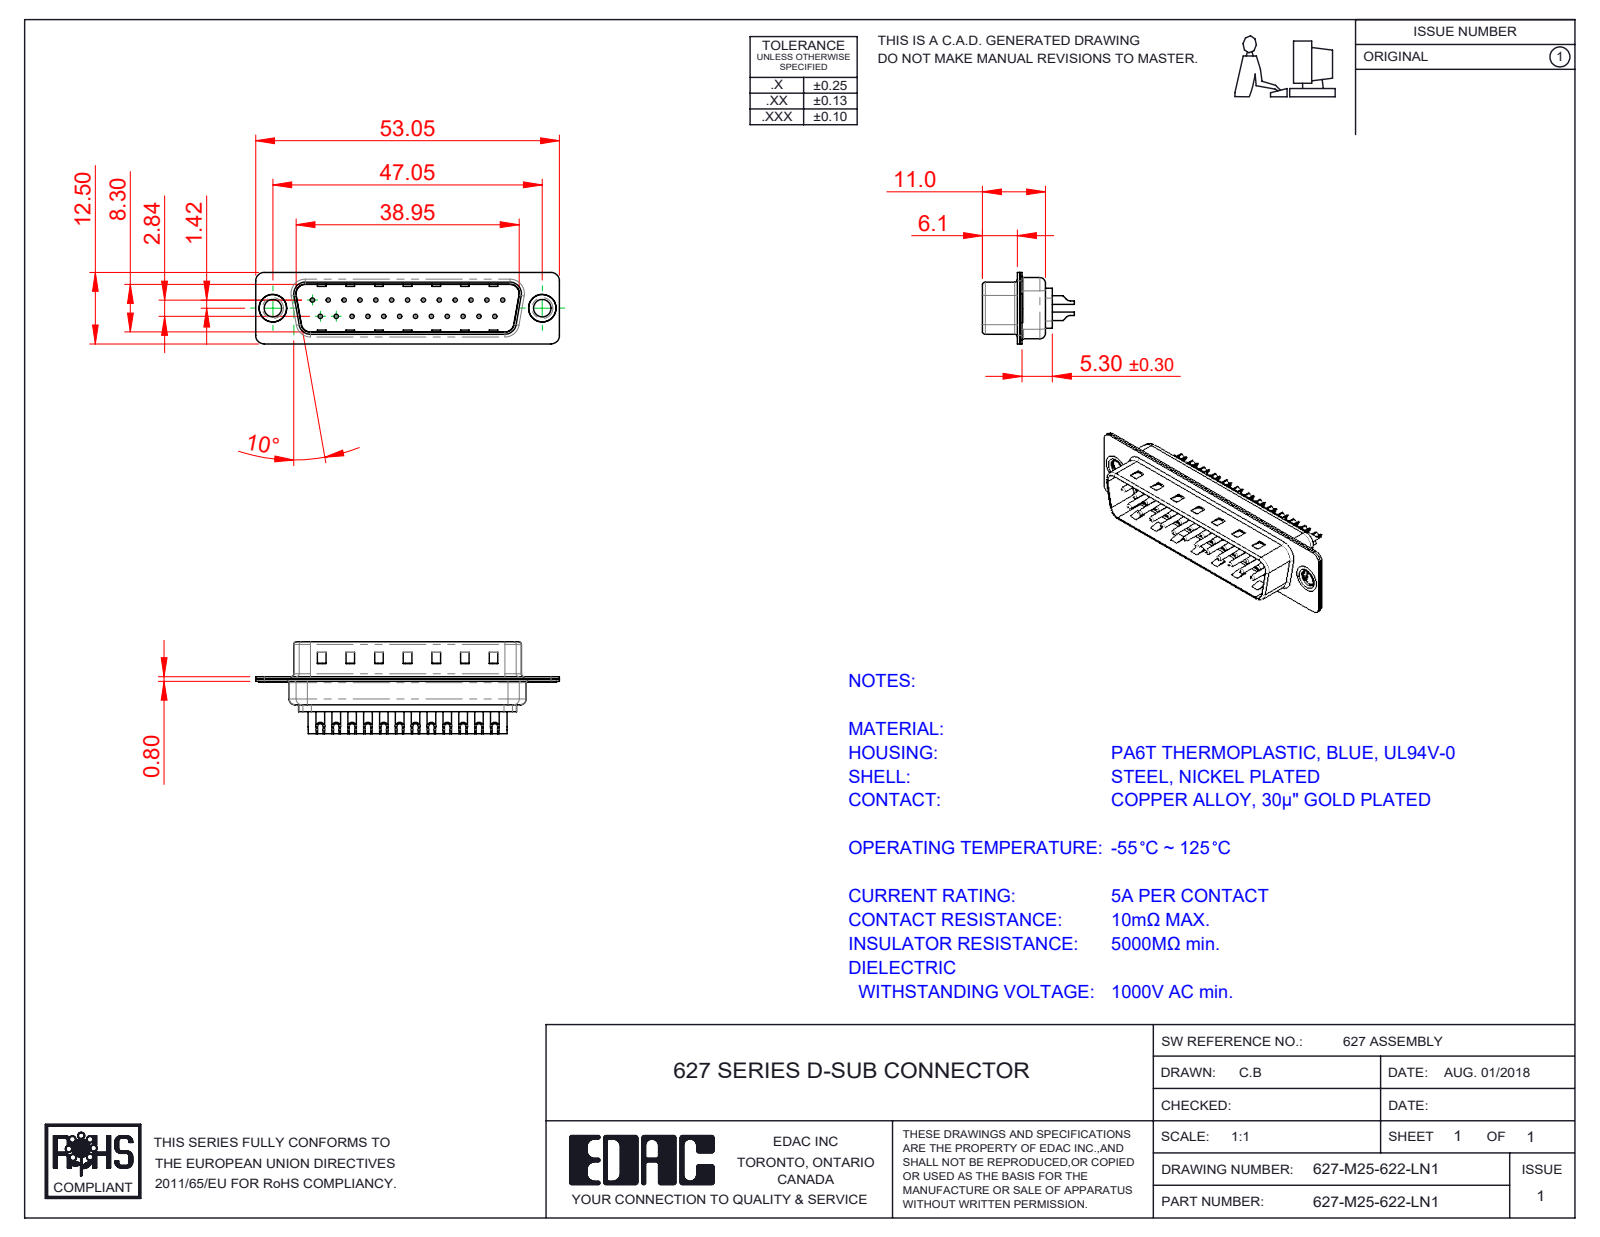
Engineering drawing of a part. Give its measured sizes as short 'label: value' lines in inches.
name: 627M Thru Hole Rivet; 627M Shell Rear_25 Contacts; 627-M25-622-LN1; 627M Contact Row 1_22 (+3 more)
written by: SolidWorks 2020 (CONFIG_CONTROL_DESIGN)
unit: in
bodies: 30 solids, 1275 faces (396 planar, 521 cylindrical, 358 other)
size: 2.089 × 0.632 × 0.492
volume: 0.165 in³; area: 10.74 in²
holes: 25× ⌀0.03, 25× ⌀0.039, 25× ⌀0.063, 25× ⌀0.079, 2× ⌀0.12, 2× ⌀0.157, 2× ⌀0.189
bosses: 25× ⌀0.059, 2× ⌀0.197, 2× ⌀0.193, 2× ⌀0.14
rounds: 16× R0.059, 12× R0.079, 8× R0.02, 8× R0.063, 6× R0.039, 4× R0.01, 4× R0.024, 4× R0.026
face distances: 0.016, 0.031, 0.374, 0.358, 0.343, 0.39, 0.047, 0.03, 0.014, 0.24
hole spacings: 0.124, 0.109, 0.218, 0.327, 0.436, 0.545, 0.654, 0.198
